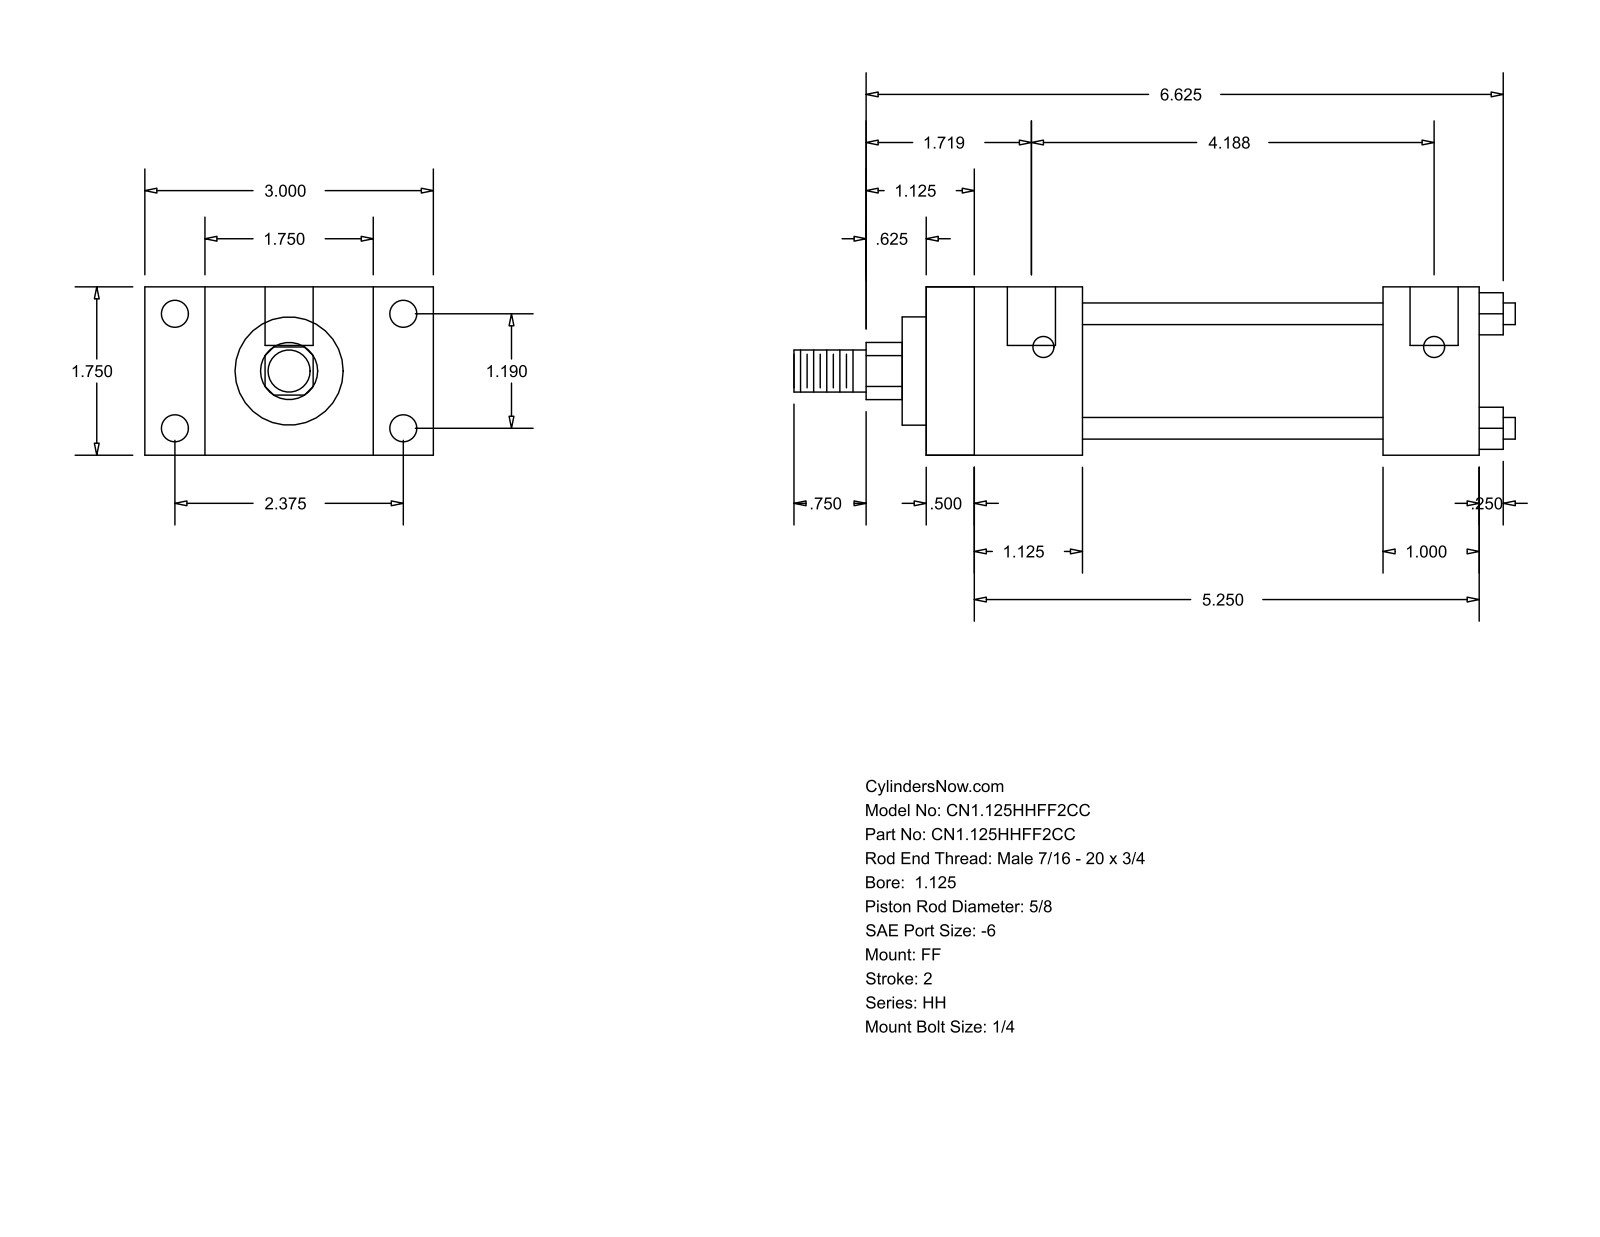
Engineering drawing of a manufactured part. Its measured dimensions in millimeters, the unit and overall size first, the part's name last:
Units: millimetres
Overall size (bounding box): 190.5 × 76.2 × 44.45
Round holes (diameter × count): ⌀5.56 ×4, ⌀7.14 ×4, ⌀12.7 ×2
Round bosses / shafts (diameter × count): ⌀5.71 ×4, ⌀34.92 ×1, ⌀28.57 ×1, ⌀15.88 ×1, ⌀11.11 ×1
Partial cylindrical surfaces — rounded edges, fillets, slot ends (radius × count): R7.54 ×1
Main face-to-face distances: 44.46, 146.05, 12.69, 133.36, 15.87, 28.58, 60.33, 25.4, 41.27, 120.65
Hole centre spacings: 30.22, 60.32, 67.47, 103.19, 3.17, 106.36
Bodies: 0 solids, 92 faces (64 planar, 28 cylindrical, 0 other)
Part name (STEP PRODUCT): HH_FF__0112_0.625
STEP written by: GSSL Pune (CONFIG_CONTROL_DESIGN)
